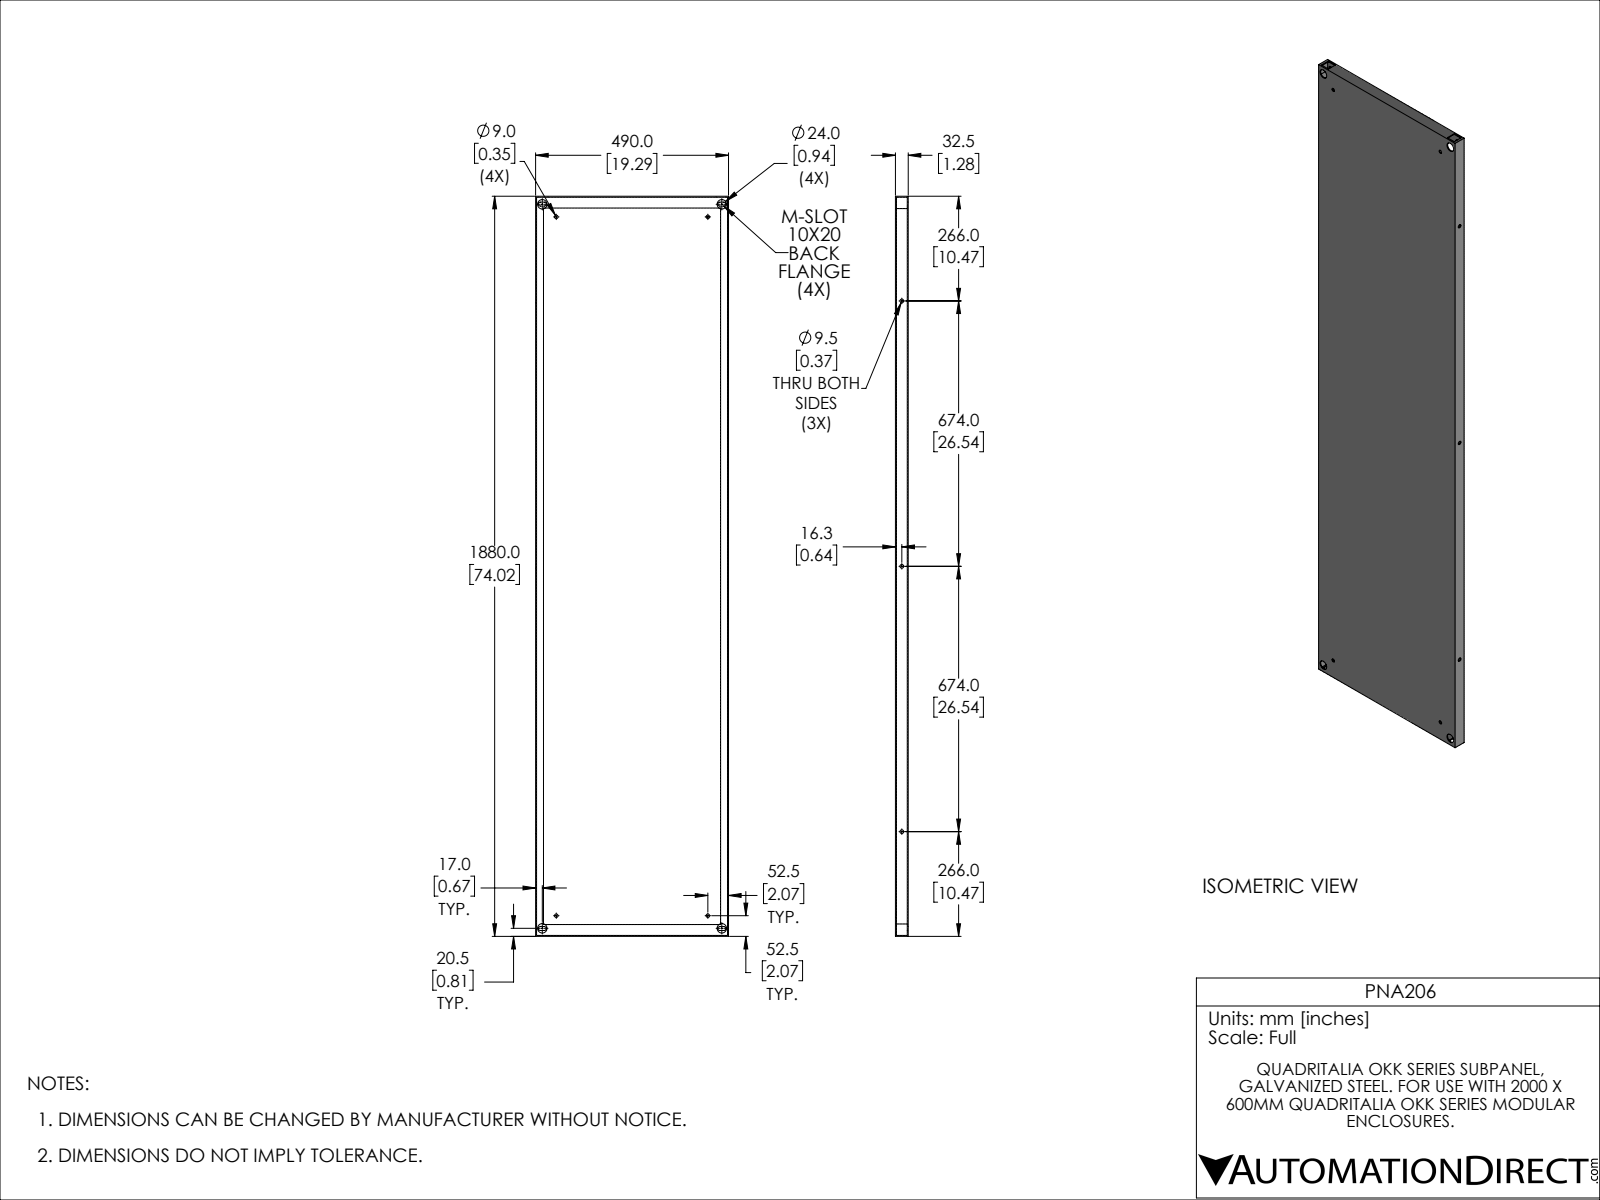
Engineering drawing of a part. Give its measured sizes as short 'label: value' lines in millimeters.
name: PNA206
written by: SolidWorks 2021 (CONFIG_CONTROL_DESIGN)
unit: mm
bodies: 1 solid, 70 faces (48 planar, 22 cylindrical, 0 other)
size: 1880 × 490 × 32.5
volume: 2 869 000 mm³; area: 2 310 000 mm²
holes: 4× ⌀9, 4× ⌀24, 3× ⌀9.5
rounds: 8× R5
face distances: 2.5, 30, 487.5, 32.5, 27.5, 490, 485, 1877.5, 1880, 1875
hole spacings: 47.8, 421.7, 1807.4, 1855.3, 385, 456, 674, 1775
